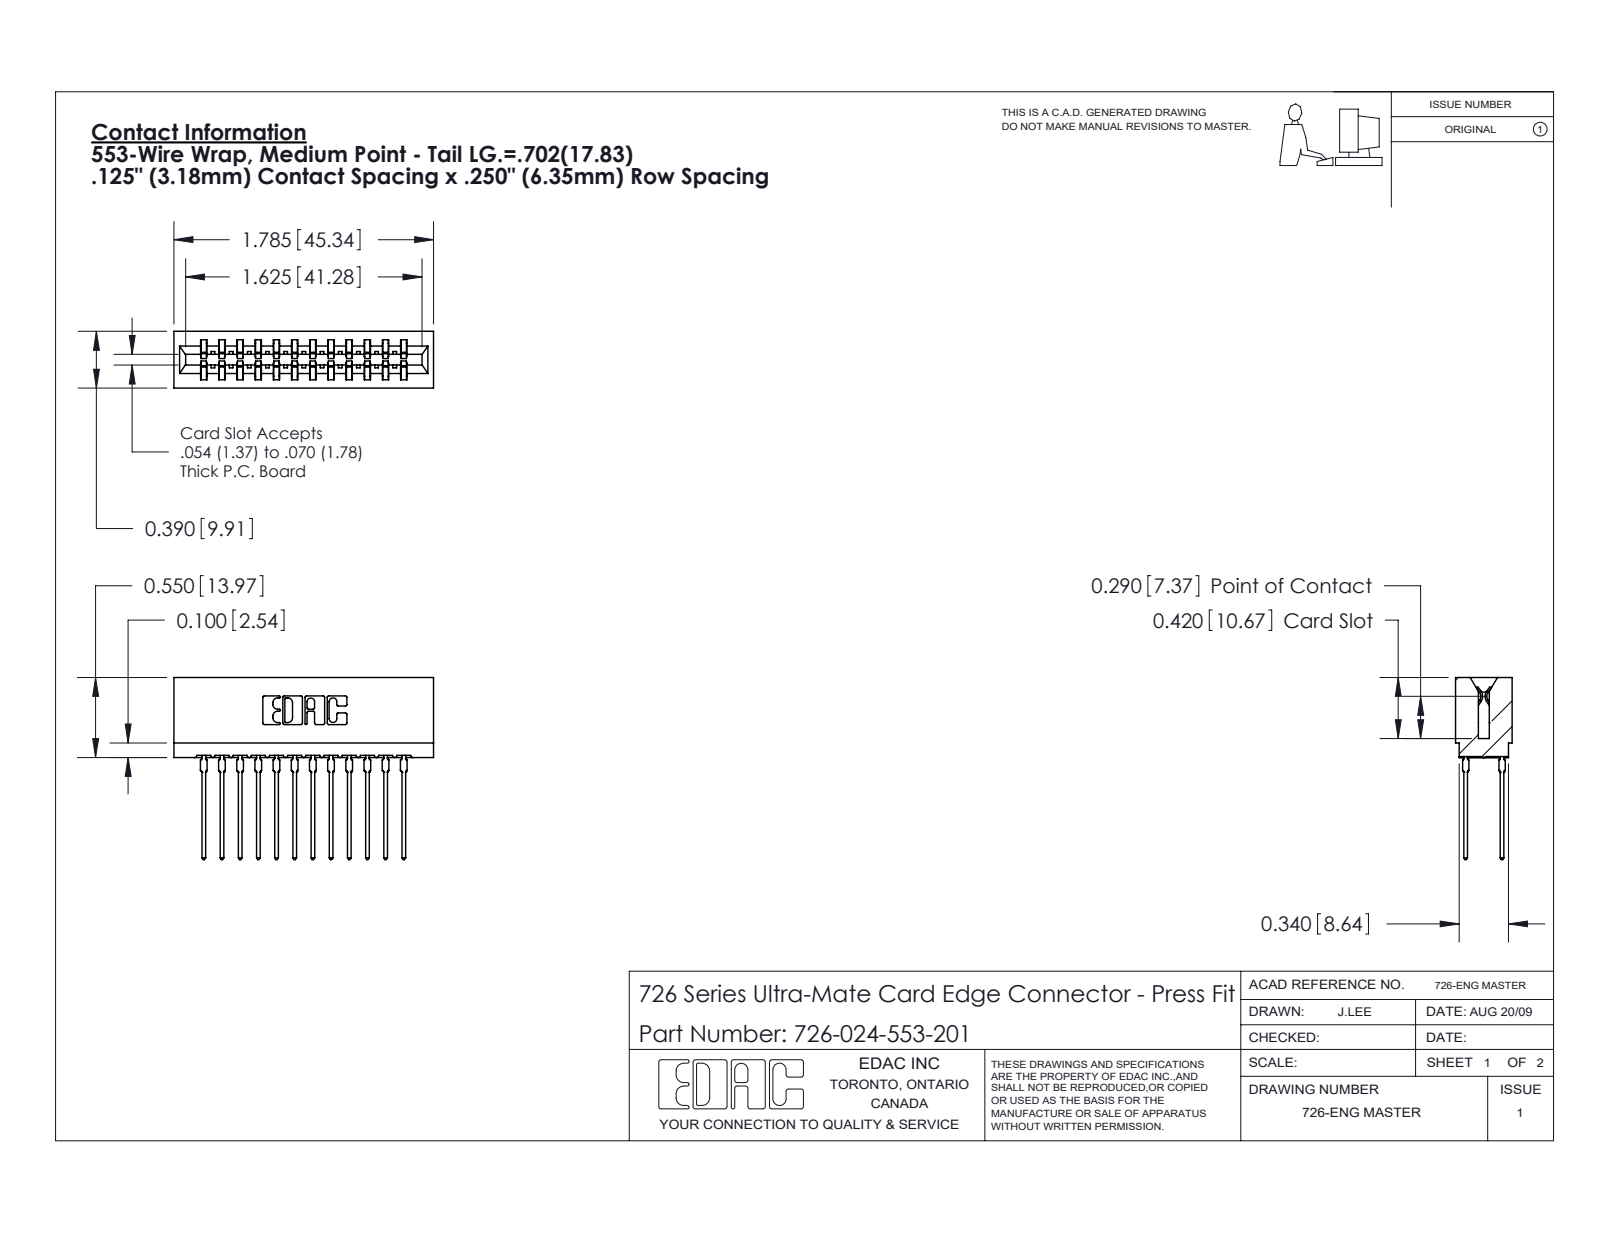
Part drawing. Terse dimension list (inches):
name: 726-024-553-201; 746-292-001_553; 726 Part_.515 Slot Depth - 01
written by: SolidWorks 2020 (CONFIG_CONTROL_DESIGN)
unit: in
bodies: 25 solids, 2245 faces (1159 planar, 462 cylindrical, 624 other)
size: 1.785 × 1.251 × 0.39
volume: 0.271 in³; area: 11.39 in²
rounds: 48× R0.021, 22× R0.01, 13× R0.015, 8× R0.005, 8× R0.011, 6× R0.007, 6× R0.031, 3× R0.026
face distances: 0.25, 0.057, 0.333, 0.025, 0.307, 0.083, 0.5, 0.39, 0.125, 0.75
